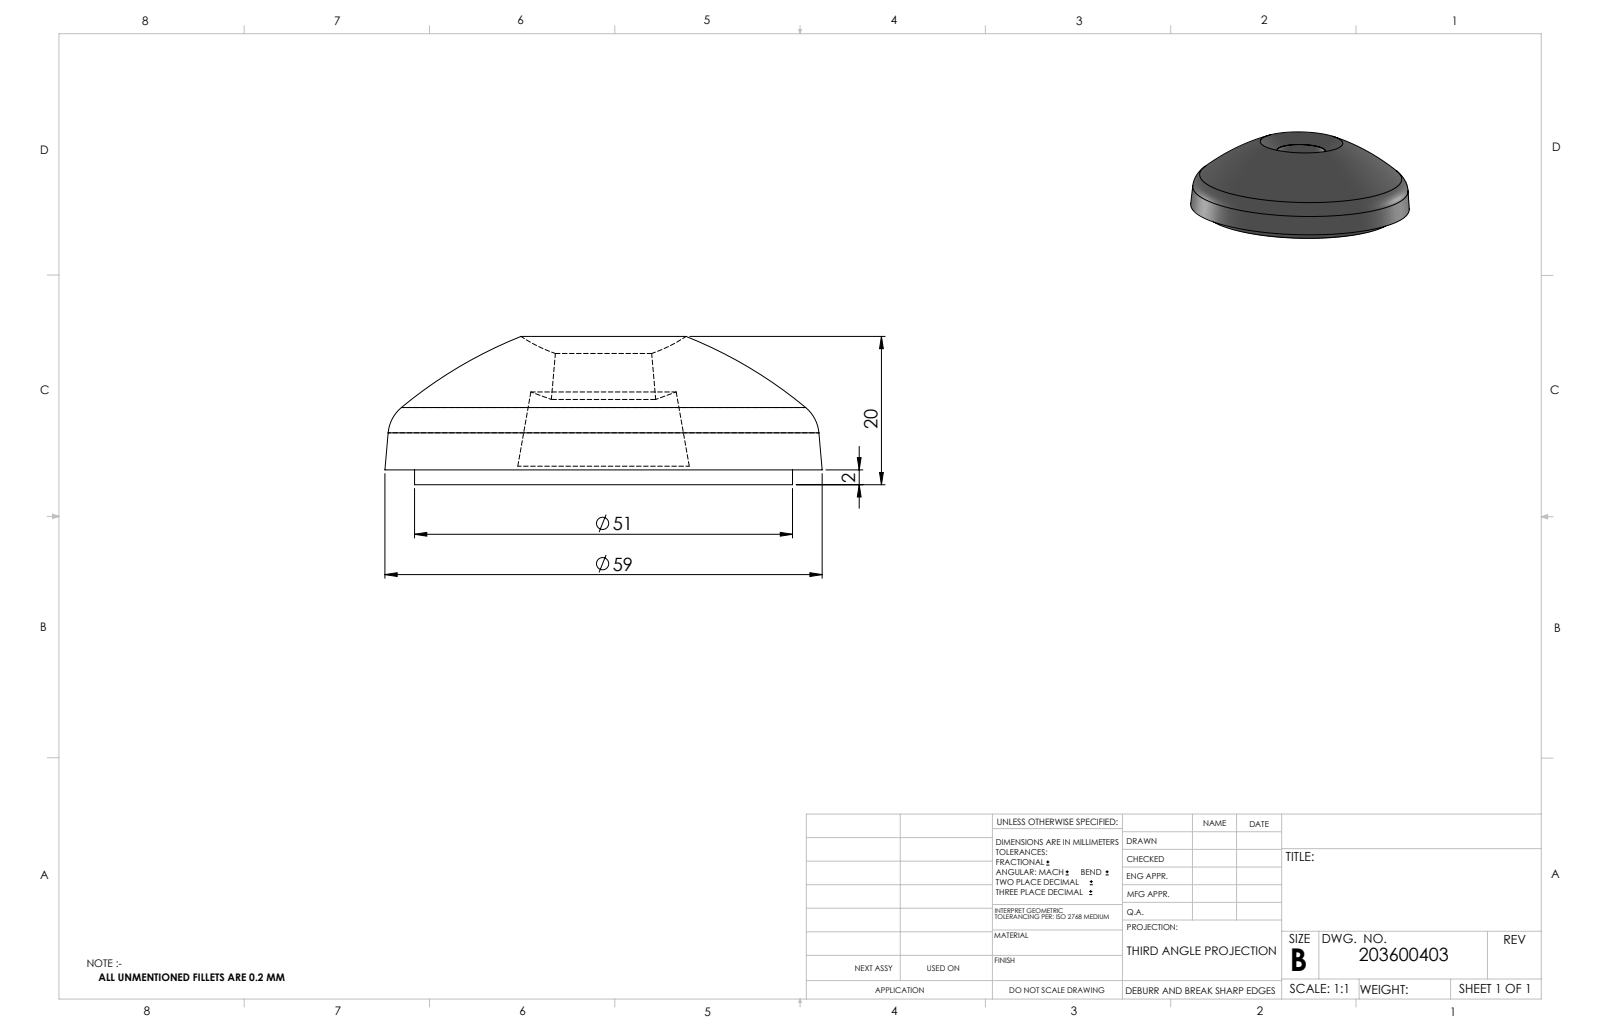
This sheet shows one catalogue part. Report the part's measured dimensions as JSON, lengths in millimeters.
{"part_name": "203600403_c_1", "step_written_by": "SolidWorks 2014 (CONFIG_CONTROL_DESIGN)", "units": "millimeters", "bodies": {"solids": 1, "faces": 19, "planar": 4, "cylindrical": 2, "other": 13}, "overall_size": [59, 59, 20], "volume_mm3": 34255, "surface_area_mm2": 8800, "round_bosses_or_shafts": [[51, 1]], "face_to_face_distances": [2, 2.5, 0.5, 17.7, 15.7, 15.2]}
